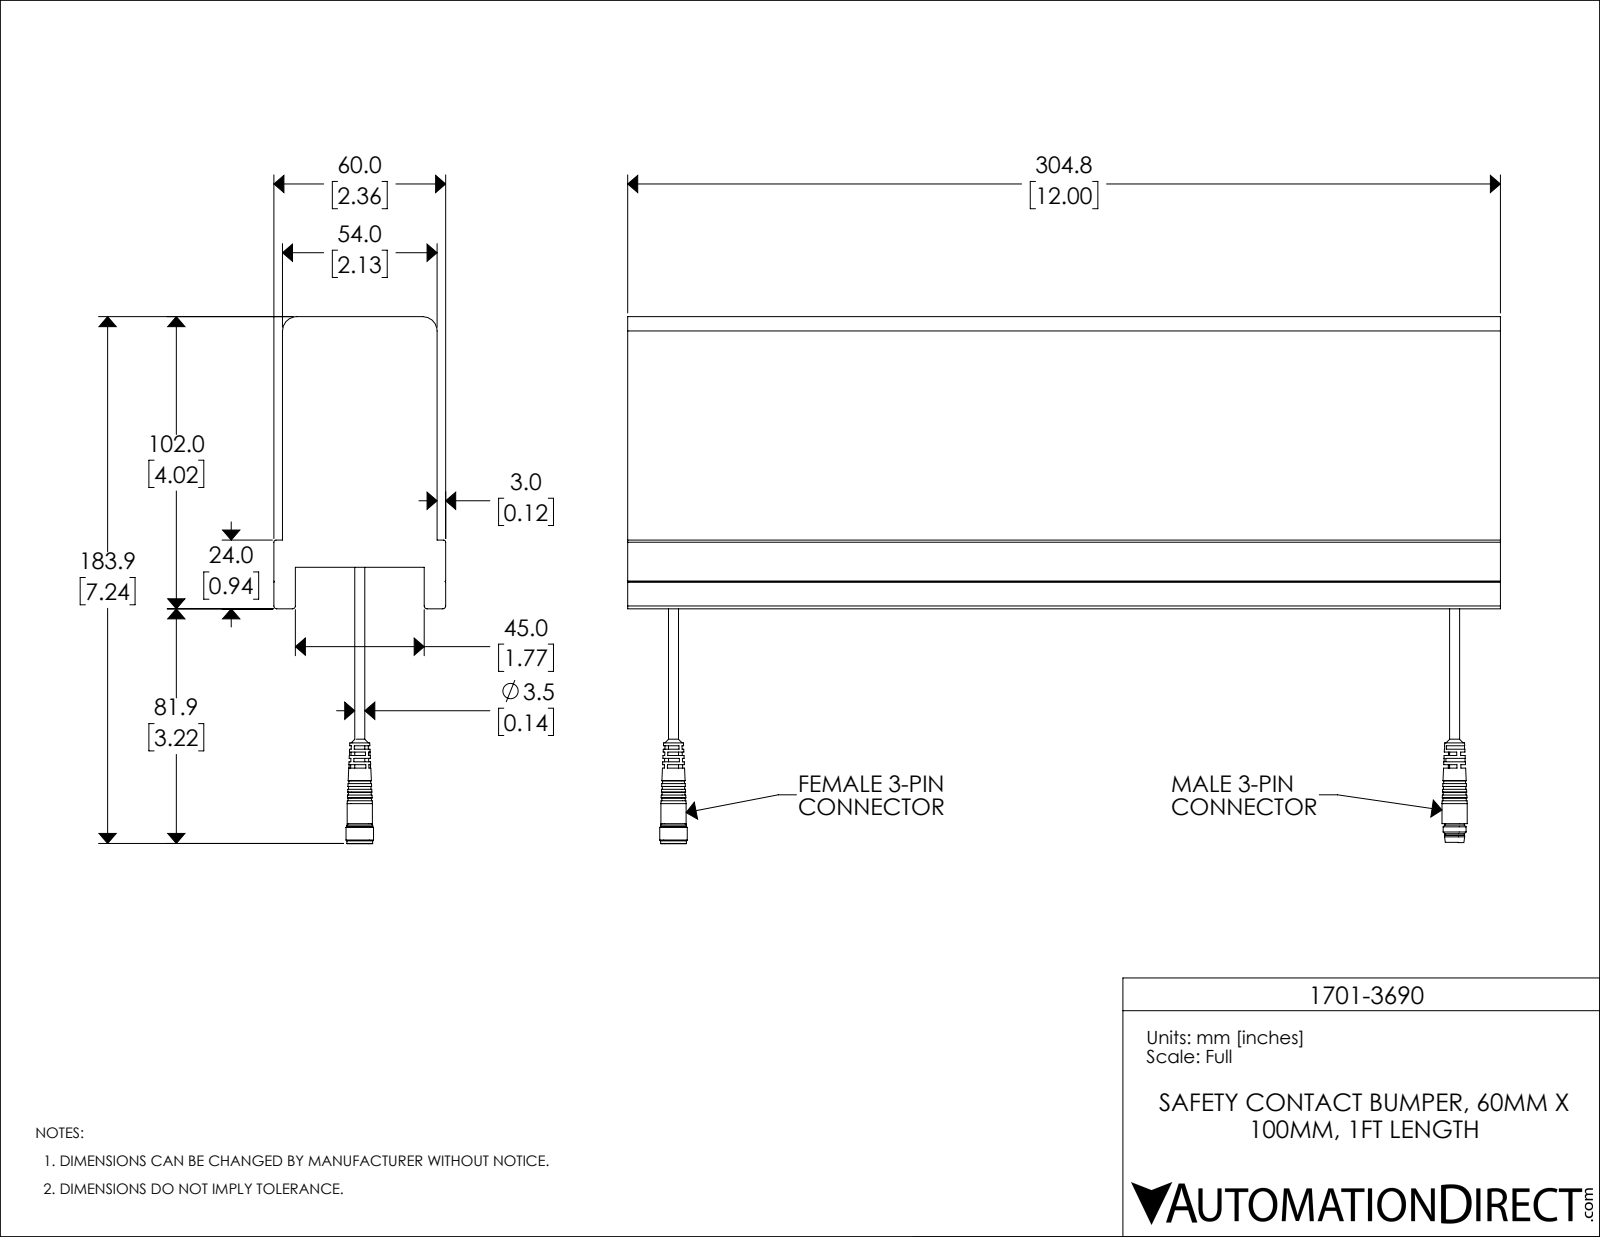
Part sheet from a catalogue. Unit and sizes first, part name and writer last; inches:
Units: inches
Overall size (bounding box): 12 × 7.244 × 2.362
Round holes (diameter × count): ⌀0.063 ×3, ⌀0.134 ×2, ⌀0.228 ×1, ⌀0.232 ×1, ⌀0.272 ×1, ⌀0.283 ×1
Round bosses / shafts (diameter × count): ⌀0.047 ×16, ⌀0.031 ×4, ⌀0.039 ×3, ⌀0.346 ×2, ⌀0.138 ×2, ⌀0.378 ×1, ⌀0.354 ×1, ⌀0.315 ×1
Main face-to-face distances: 2.126, 3.445, 0.118, 2.244, 0.295, 2.067, 0.177, 1.949, 2.362, 12
Hole centre spacings: 0.069, 0.098, 10.789, 0.138, 10.691, 10.74
Volume: 93.04 in³ · Surface area: 187.7 in²
Bodies: 20 solids, 294 faces (138 planar, 59 cylindrical, 97 other)
Part name (STEP PRODUCT): 1701-3690
STEP written by: SolidWorks 2018 (AUTOMOTIVE_DESIGN)
